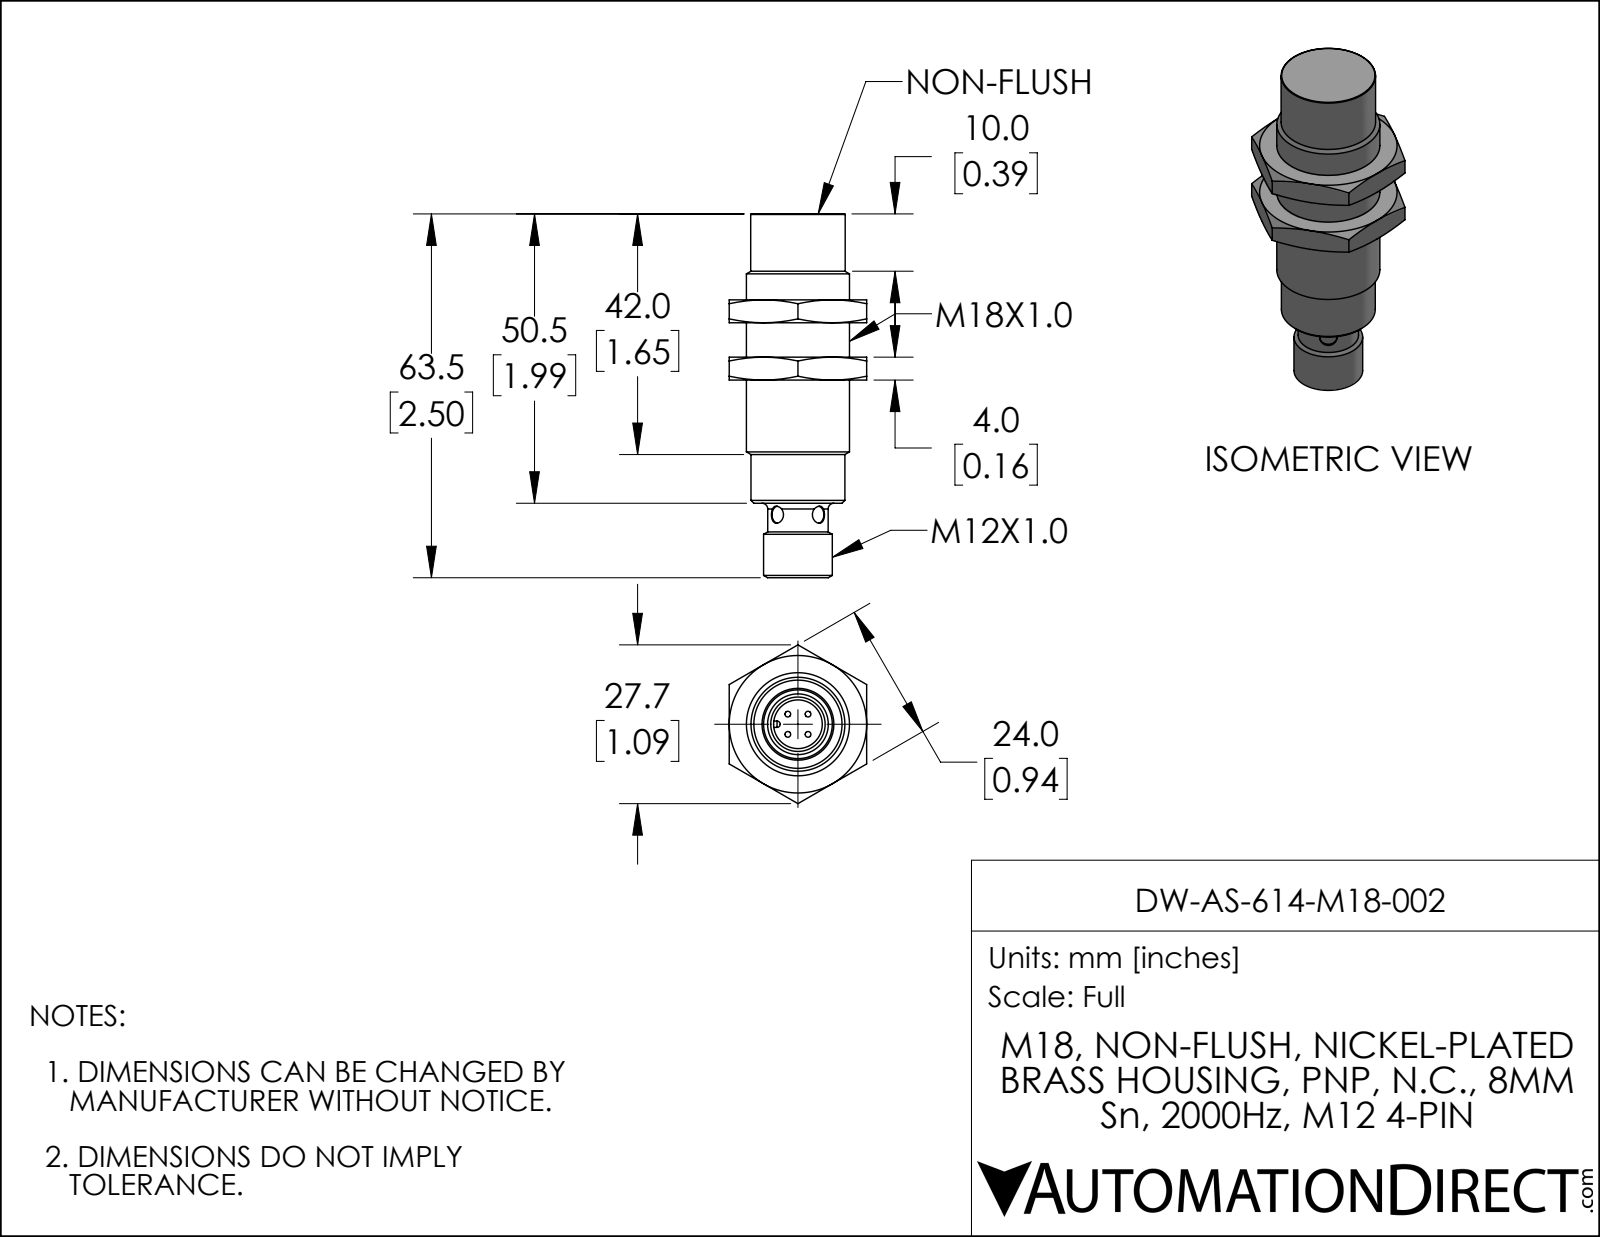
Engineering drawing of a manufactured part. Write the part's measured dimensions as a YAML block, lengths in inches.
part_name: "DW-AS-614-M18-002"
step_written_by: "SolidWorks 2019 (AUTOMOTIVE_DESIGN)"
units: inches
bodies: {solids: 1, faces: 82, planar: 27, cylindrical: 18, other: 37}
overall_size: [2.5, 1.091, 0.945]
volume: 0.905
surface_area: 8.001
round_holes:
  - {diameter: 0.118, count: 2}
  - {diameter: 0.335, count: 1}
round_bosses_or_shafts:
  - {diameter: 0.039, count: 4}
  - {diameter: 0.709, count: 1}
  - {diameter: 0.65, count: 1}
  - {diameter: 0.646, count: 1}
  - {diameter: 0.472, count: 1}
  - {diameter: 0.415, count: 1}
partial_cylinders:
  - {radius: 0.022, count: 2}
face_to_face_distances: [0.394, 0.157, 0.945, 0.591, 0.748, 0.984, 1.142, 0.551, 0.236, 1.988]
